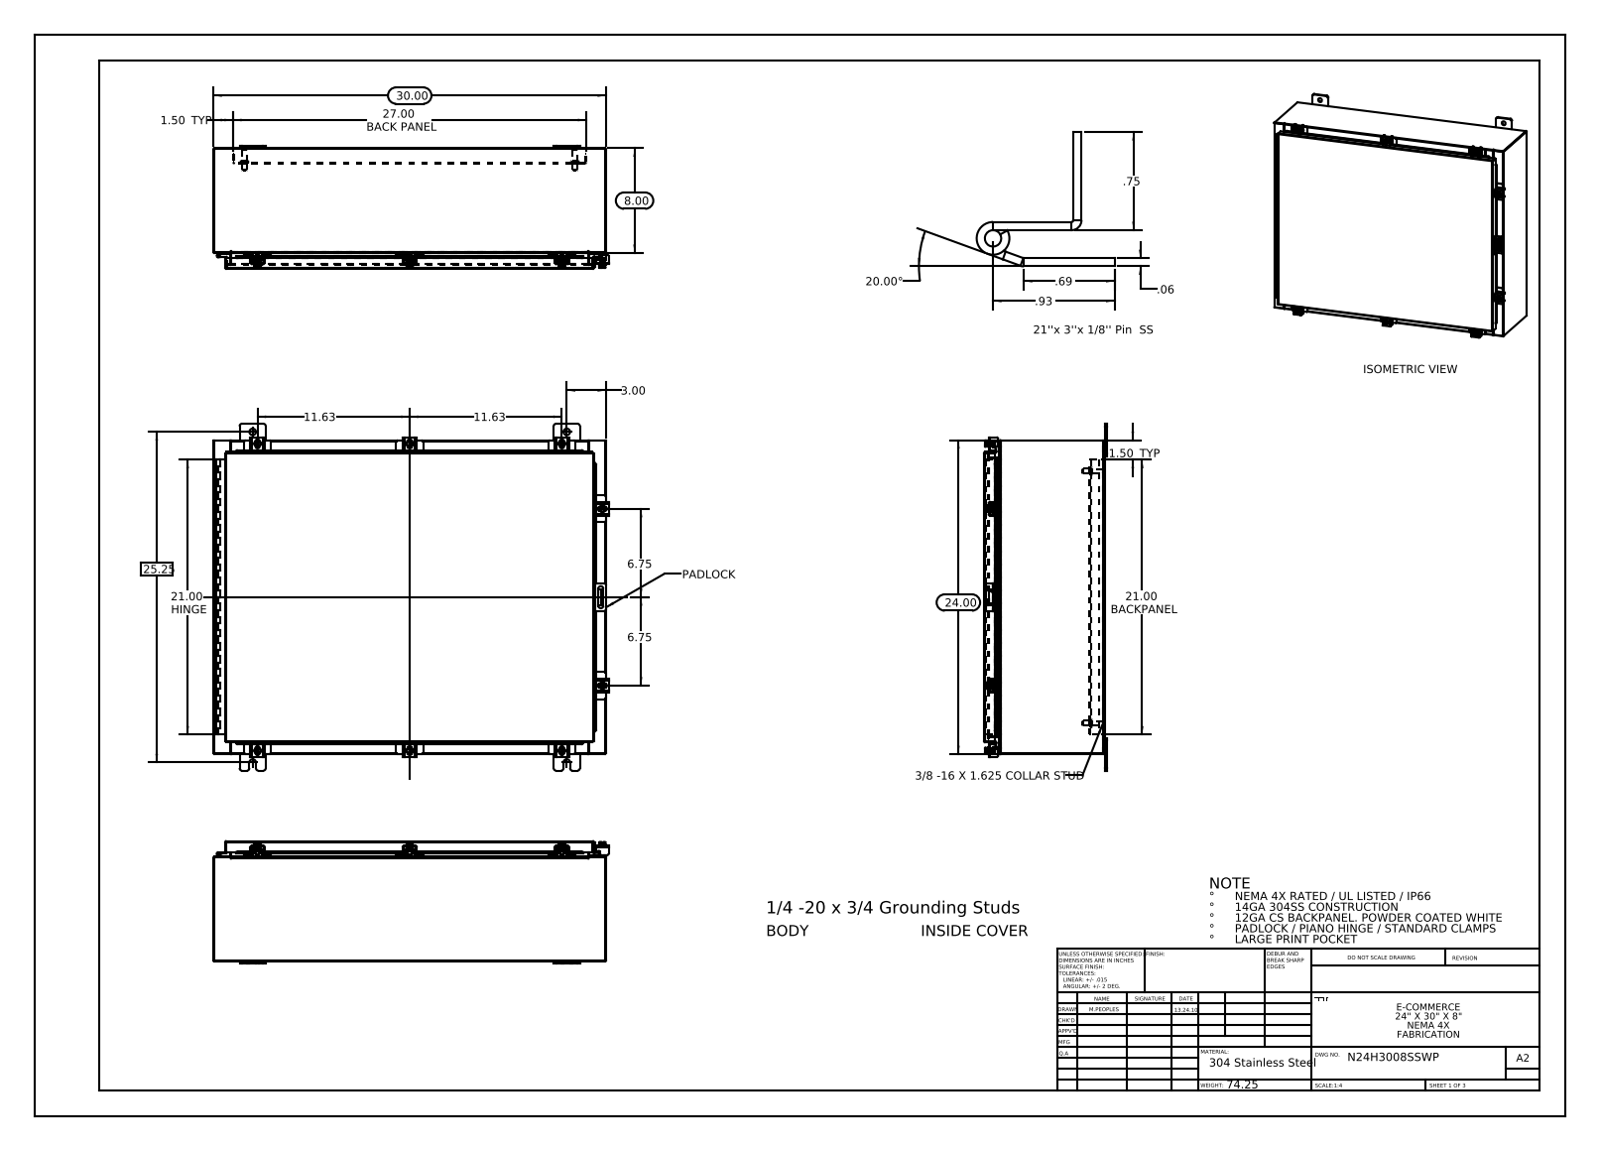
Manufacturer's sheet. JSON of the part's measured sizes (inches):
{"part_name": "N24H3008SSWP; N24H3008SSWP Cover; N24H3008SSWP Clamp Top; N24H3008SSWP Top (+8 more)", "step_written_by": "SolidWorks 2013 (CONFIG_CONTROL_DESIGN)", "units": "inches", "bodies": {"solids": 57, "faces": 1943, "planar": 1028, "cylindrical": 803, "other": 112}, "overall_size": [30.211, 26.5, 9.389], "volume_in3": 260.9, "surface_area_in2": 6534, "round_holes": [[0.213, 8], [0.26, 8], [0.5, 8], [0.125, 2], [0.125, 1]], "round_bosses_or_shafts": [[0.25, 9], [0.5, 8], [0.399, 8], [0.625, 4], [0.375, 4], [0.33, 4]], "partial_cylinders_radius": [[0.06, 38], [0.013, 25], [0.19, 24], [0.088, 21], [0.12, 16], [0.141, 16], [0.05, 11], [0.08, 10]], "face_to_face_distances": [0.075, 9.126, 9.201, 9.051, 0.104, 1, 1.075, 8.051, 8.126, 1.179], "hole_center_spacings": [21.374, 24, 26.174, 23.451, 1.858, 2.326, 2.326, 3.065]}
